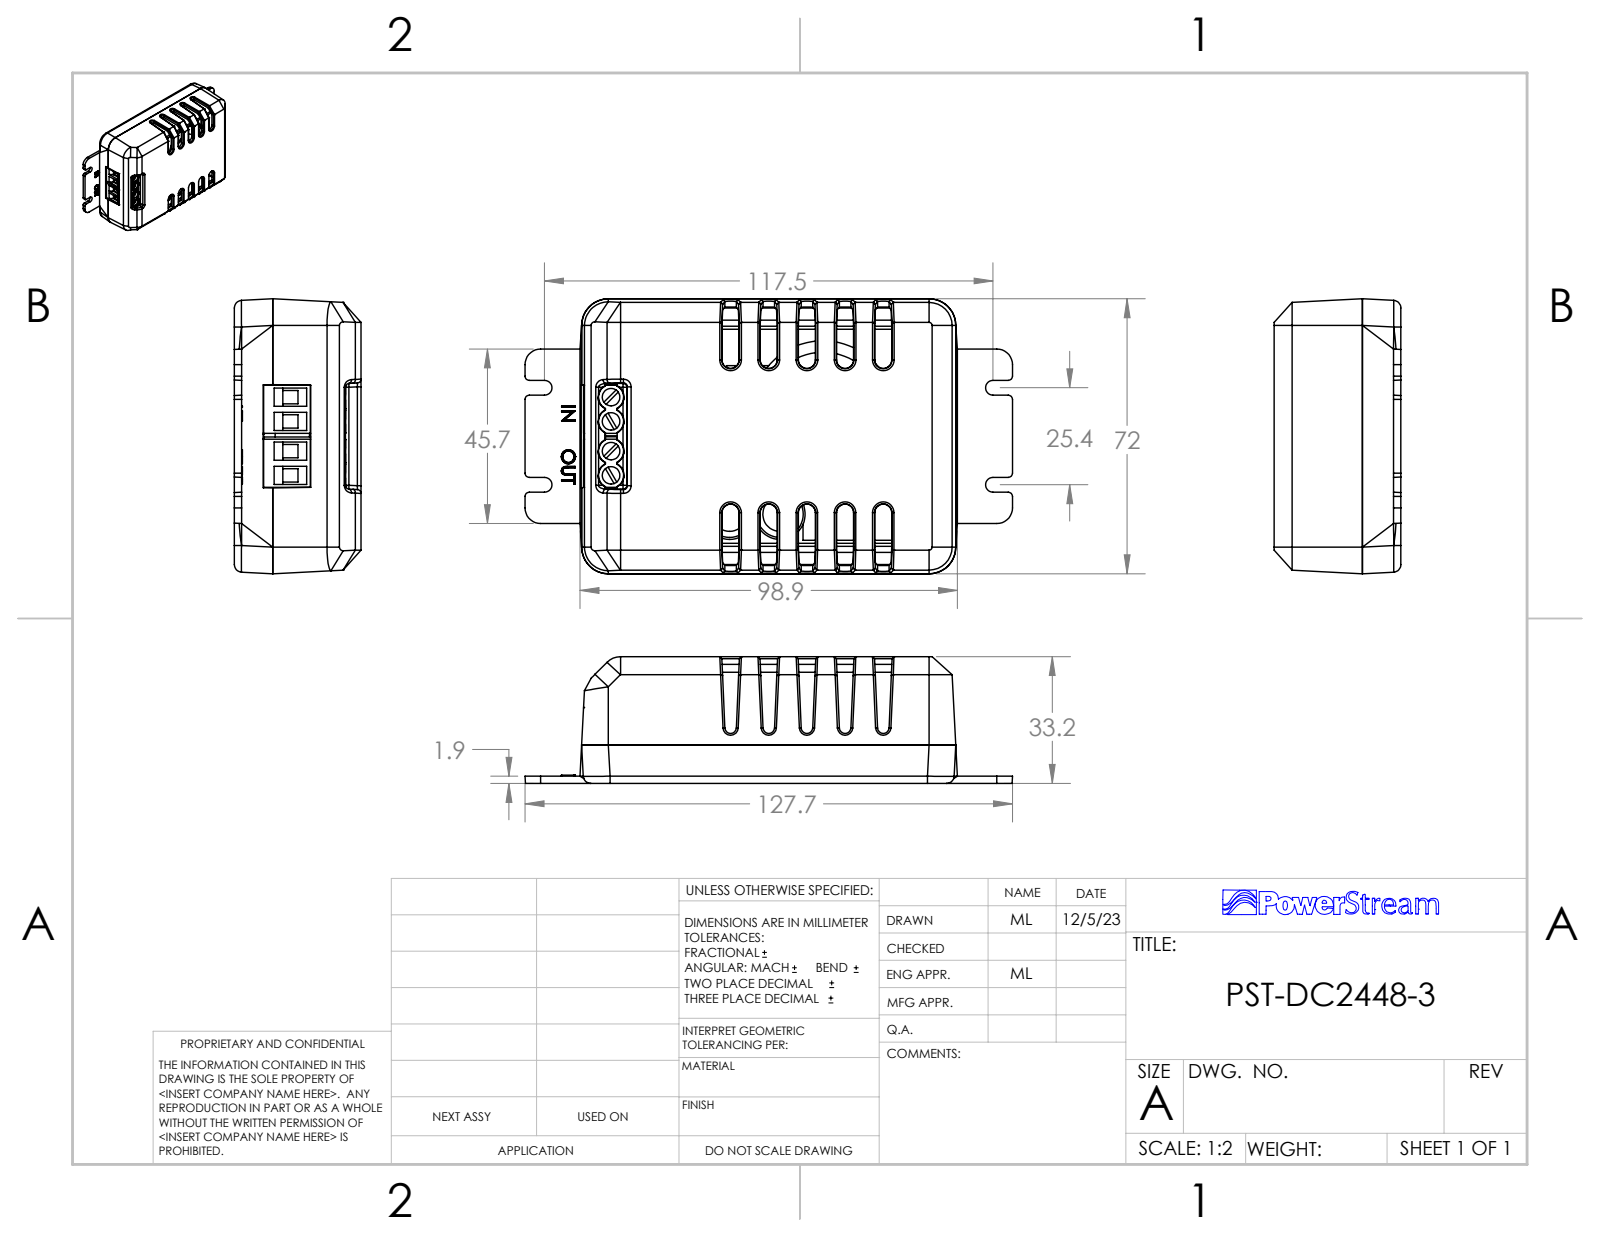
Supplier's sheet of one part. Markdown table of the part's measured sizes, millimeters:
| quantity | value |
| --- | --- |
| part name | PST-DC2448-3; Case2; 219-263a; M2.5 Phillips 99461A935 |
| STEP written by | SolidWorks 2018 (AUTOMOTIVE_DESIGN) |
| units | millimeters |
| bodies | 63 solids, 2029 faces (1221 planar, 444 cylindrical, 364 other) |
| overall size | 127.67 × 72 × 33.19 |
| volume | 112 536 mm³ |
| surface area | 102 691 mm² |
| round holes (diameter × count) | 2 × 4, 3 × 4, 4.6 × 4, 1.88 × 1, 13.5 × 1 |
| round bosses / shafts (diameter × count) | 0.8 × 16, 13.18 × 8, 4.4 × 4, 2.5 × 4, 1.4 × 4, 37.6 × 1 |
| partial cylindrical surfaces (radius × count) | 0.5 × 63, 0.45 × 24, 0.65 × 16, 0.7 × 14, 1 × 11, 0.25 × 8, 3 × 6, 1.5 × 5 |
| main face-to-face distances | 2, 31.19, 1.59, 4.09, 6.09, 2.4, 4, 5.69, 7.69, 1.6 |
| hole center spacings | 1.61, 1.62, 6.35, 6.59, 7.68, 7.69, 8.88, 12.9 |
